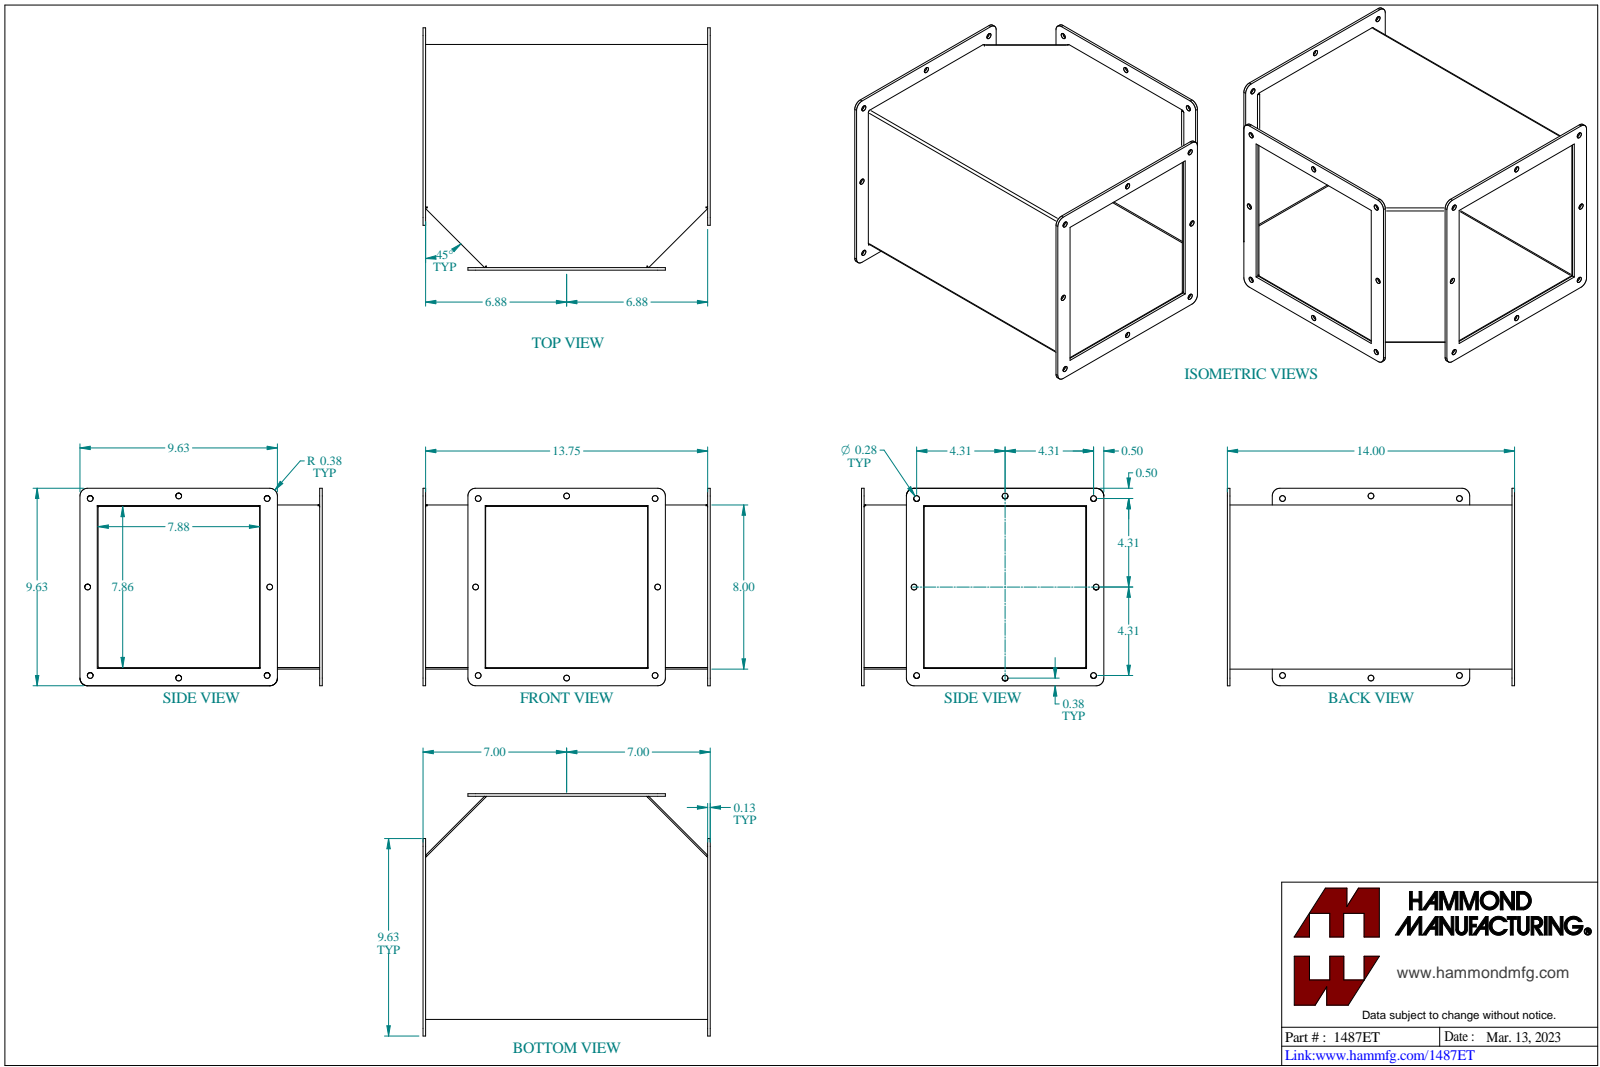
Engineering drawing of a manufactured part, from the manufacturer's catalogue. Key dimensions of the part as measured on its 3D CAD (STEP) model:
Part name (STEP PRODUCT): 1487ET
STEP written by: SolidWorks 2023 (CONFIG_CONTROL_DESIGN)
Units: inches
Bodies: 5 solids, 166 faces (74 planar, 92 cylindrical, 0 other)
Overall size (bounding box): 14.125 × 11.811 × 9.628
Volume: 47.1 in³ · Surface area: 1 184 in²
Round holes (diameter × count): ⌀0.281 ×24
Partial cylindrical surfaces — rounded edges, fillets, slot ends (radius × count): R0.375 ×12, R0.036 ×4, R0.108 ×4, R0.25 ×4
Main face-to-face distances: 0.072, 7.928, 8, 7.856, 0.125, 0.125, 13.875, 14, 10.875, 10.803
Hole centre spacings: 4.315, 9.755, 8.625, 6.276, 8.875, 12.198, 4.311, 4.314
